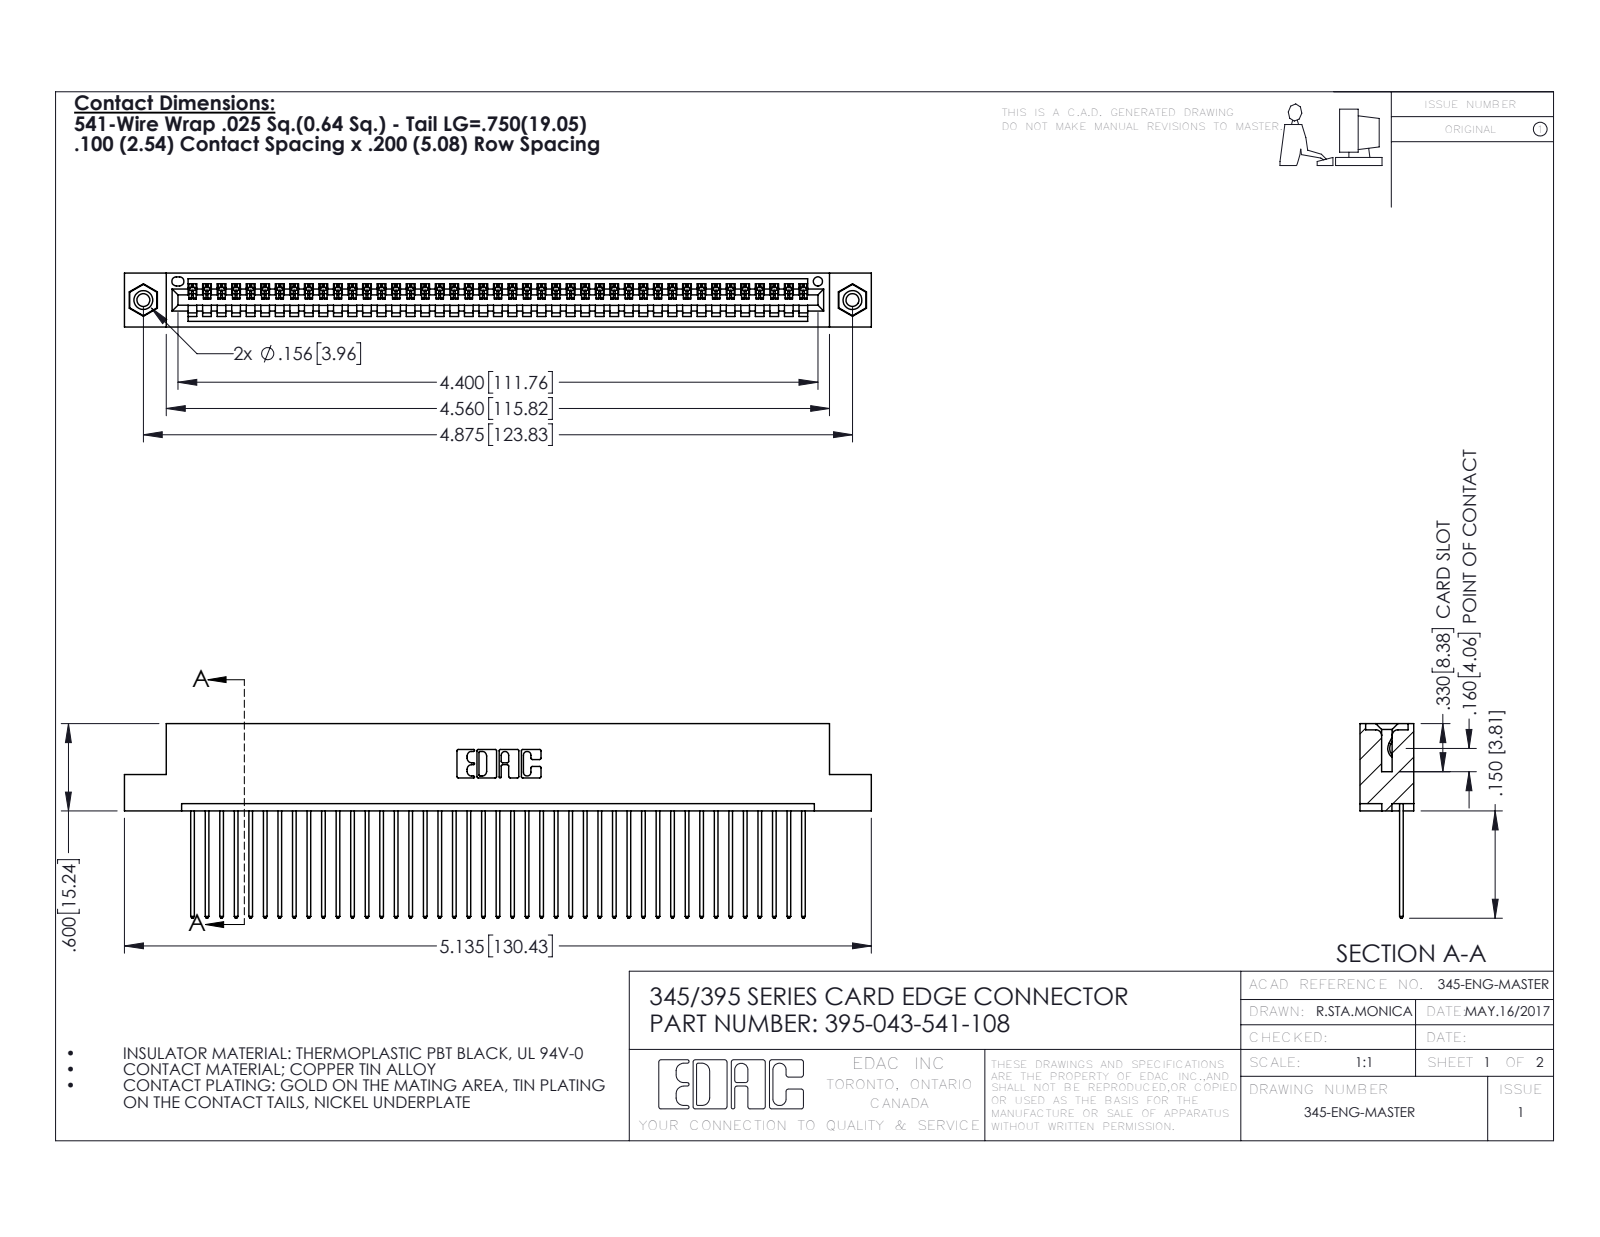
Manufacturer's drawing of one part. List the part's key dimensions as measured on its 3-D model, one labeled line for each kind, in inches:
Part name (STEP PRODUCT): 345-292-001_345-293-141; 345-250-001_345-250-003-102; 345 Part_Flush Mounting Lugs - 0.156 Dia-TI; 395-043-541-108
STEP written by: SolidWorks 2016 (CONFIG_CONTROL_DESIGN)
Units: inches
Bodies: 46 solids, 2680 faces (1832 planar, 832 cylindrical, 16 other)
Overall size (bounding box): 5.135 × 1.337 × 0.37
Volume: 0.765 in³ · Surface area: 27.16 in²
Round holes (diameter × count): ⌀0.089 ×2, ⌀0.125 ×2, ⌀0.156 ×2, ⌀0.064 ×1
Round bosses / shafts (diameter × count): ⌀0.155 ×2
Partial cylindrical surfaces — rounded edges, fillets, slot ends (radius × count): R0.006 ×86, R0.01 ×86, R0.01 ×22, R0.007 ×6, R0.031 ×6, R0.026 ×3, R0.031 ×2, R0.04 ×2
Main face-to-face distances: 0.072, 0.298, 0.098, 0.272, 0.025, 0.37, 0.2, 0.225, 0.149, 0.072
Hole centre spacings: 0.27, 4.639, 4.875
